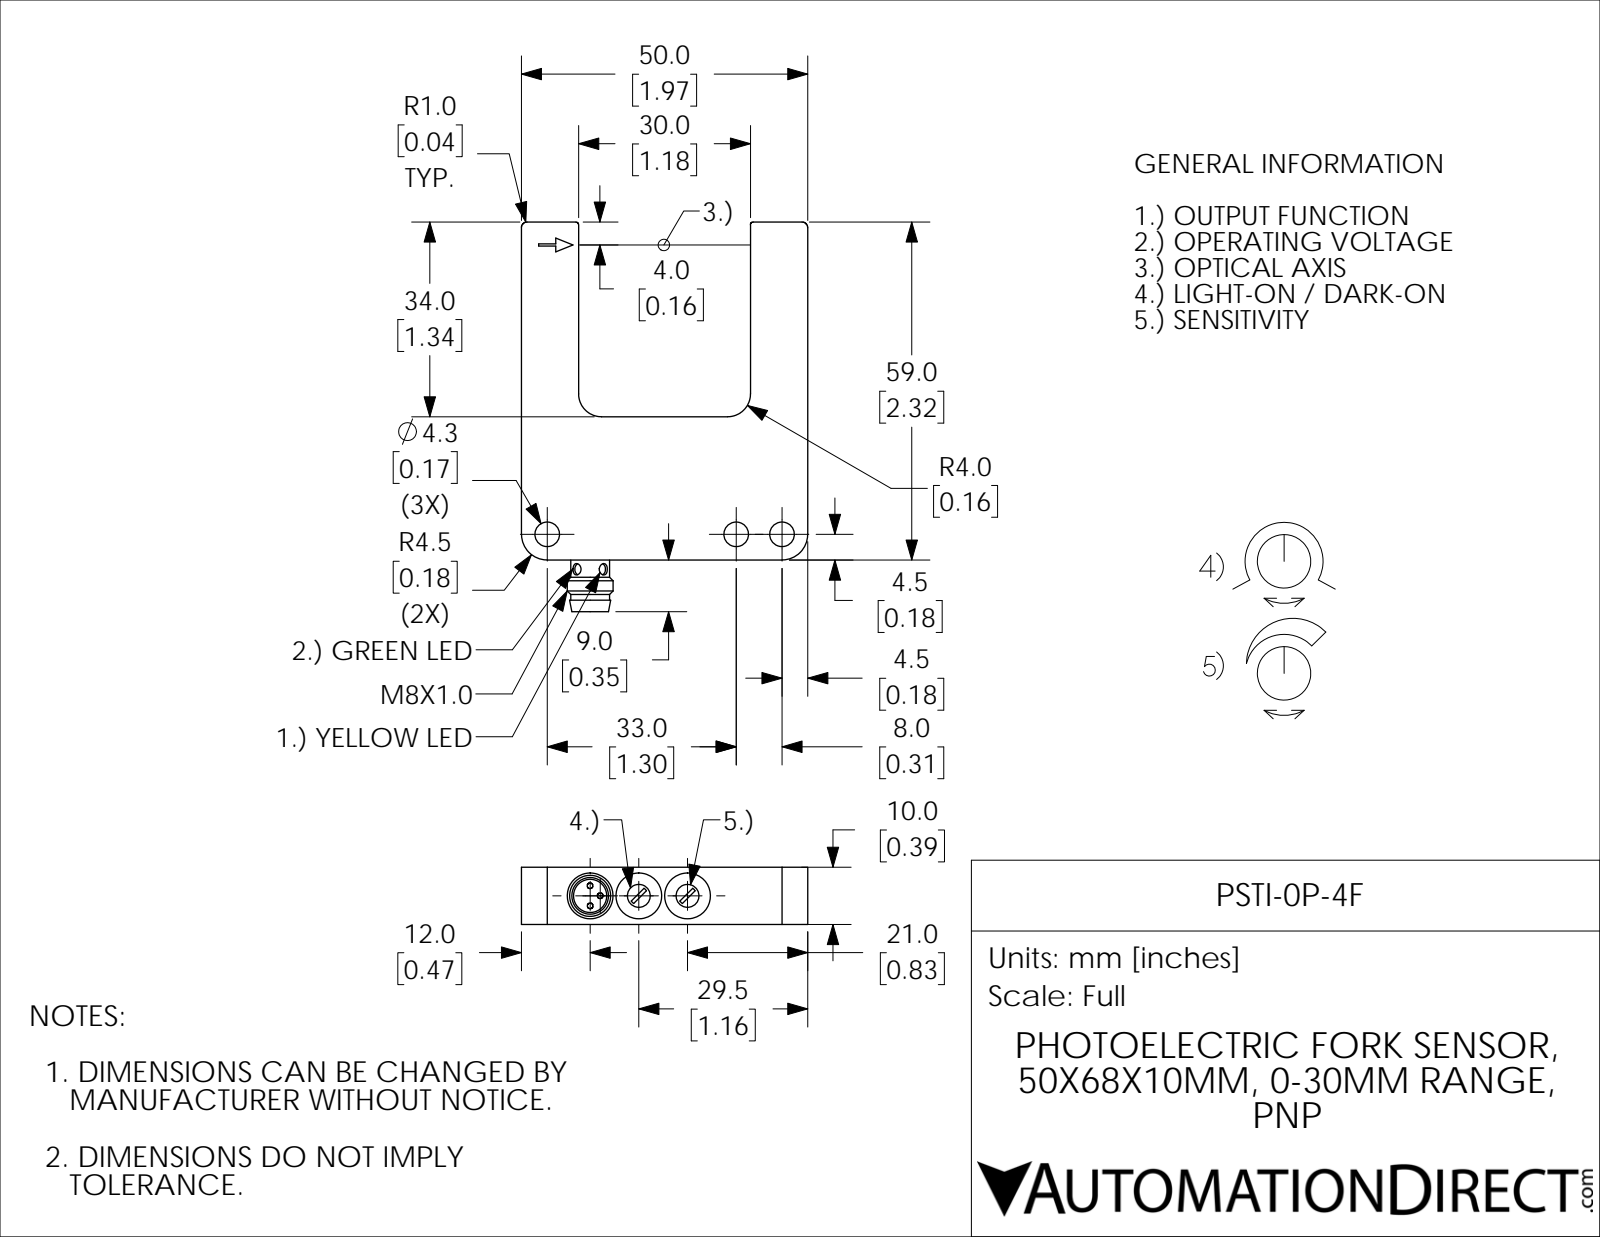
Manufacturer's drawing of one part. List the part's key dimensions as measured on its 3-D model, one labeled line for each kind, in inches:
Part name (STEP PRODUCT): PSTI-0P-4F
STEP written by: SolidWorks 2017 (AUTOMOTIVE_DESIGN)
Units: inches
Bodies: 1 solid, 71 faces (35 planar, 30 cylindrical, 6 other)
Overall size (bounding box): 2.677 × 1.969 × 0.394
Volume: 1.163 in³ · Surface area: 11.35 in²
Round holes (diameter × count): ⌀0.169 ×3, ⌀0.079 ×2, ⌀0.157 ×2, ⌀0.315 ×2, ⌀0.228 ×1
Round bosses / shafts (diameter × count): ⌀0.039 ×3, ⌀0.315 ×1, ⌀0.267 ×1
Partial cylindrical surfaces — rounded edges, fillets, slot ends (radius × count): R0.02 ×2, R0.039 ×2, R0.063 ×2, R0.157 ×2, R0.177 ×2
Main face-to-face distances: 0.394, 1.575, 1.969, 1.181, 0.984, 1.339, 2.323, 2.319, 0.98, 0.157
Hole centre spacings: 0.335, 0.315, 0.669, 1.299, 1.614
